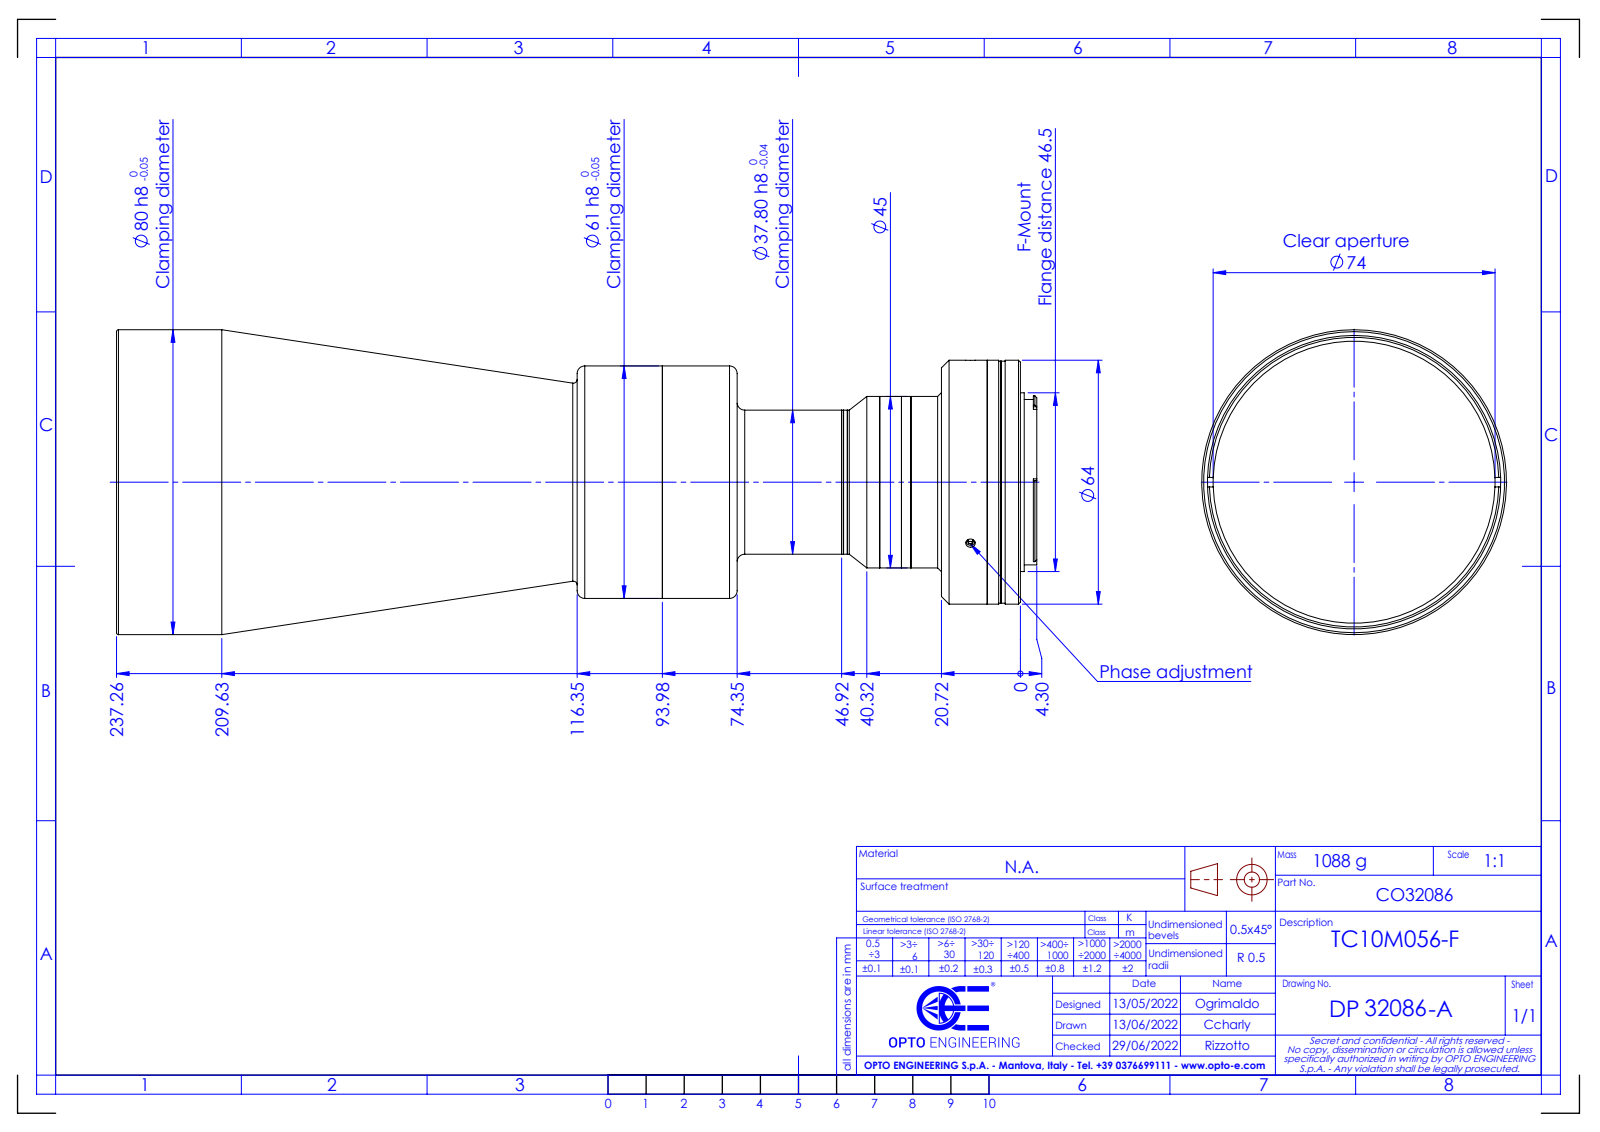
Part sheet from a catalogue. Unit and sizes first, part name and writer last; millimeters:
Units: millimetres
Overall size (bounding box): 241.56 × 80 × 80
Round holes (diameter × count): ⌀2.5 ×3, ⌀33 ×1, ⌀42 ×1, ⌀53 ×1, ⌀74 ×1, ⌀77 ×1
Round bosses / shafts (diameter × count): ⌀80 ×1, ⌀64 ×1, ⌀63.5 ×1, ⌀61 ×1, ⌀46.9 ×1, ⌀45 ×1, ⌀43.4 ×1, ⌀37.8 ×1
Partial cylindrical surfaces — rounded edges, fillets, slot ends (radius × count): R0.5 ×5, R1.15 ×2, R22.65 ×1
Main face-to-face distances: 1, 5, 5.7, 15.02, 20.72, 16.72, 1.7, 4, 15.72, 0.7
Bodies: 0 solids, 149 faces (43 planar, 68 cylindrical, 38 other)
Part name (STEP PRODUCT): DP32086-A_TC10M056-F
STEP written by: SolidWorks 2021 (CONFIG_CONTROL_DESIGN)
